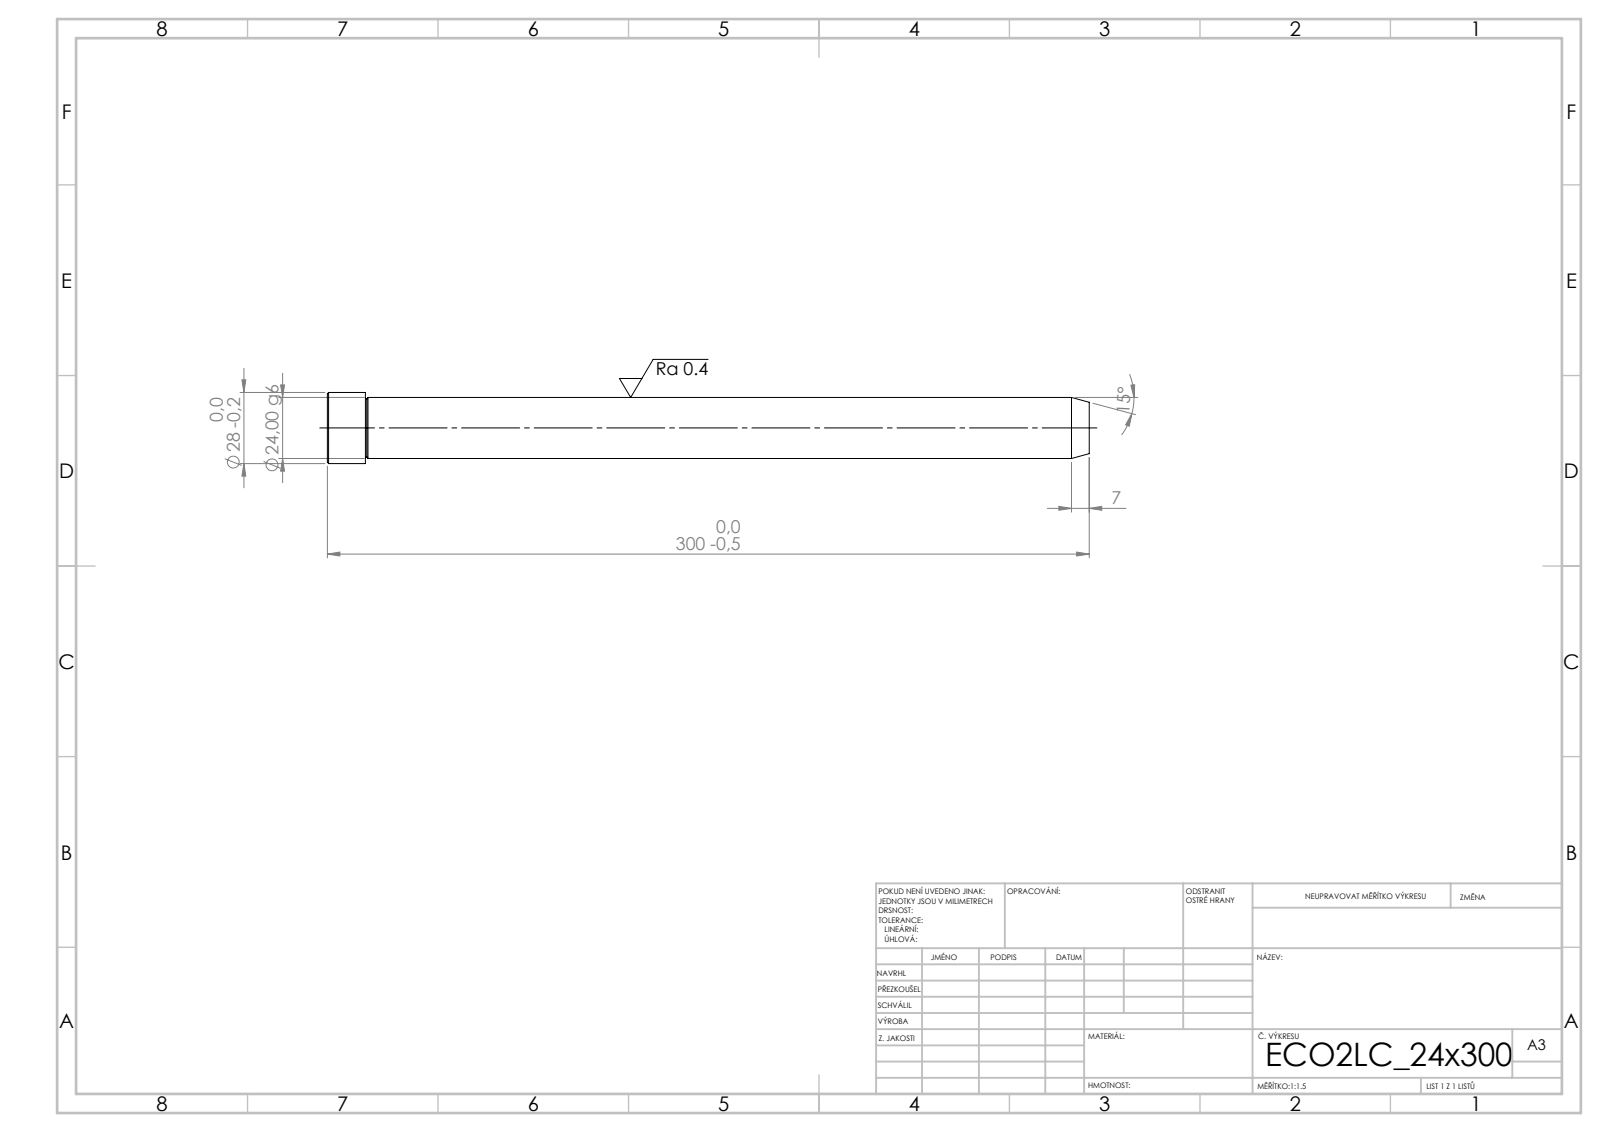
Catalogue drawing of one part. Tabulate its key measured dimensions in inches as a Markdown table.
| quantity | value |
| --- | --- |
| STEP written by | SolidWorks 2019 (CONFIG_CONTROL_DESIGN) |
| units | inches |
| bodies | 1 solid, 15 faces (3 planar, 4 cylindrical, 8 other) |
| overall size | 11.811 × 1.102 × 1.102 |
| volume | 8.4 in³ |
| surface area | 37.04 in² |
| round bosses / shafts (diameter × count) | 1.102 × 1, 0.945 × 1 |
| main face-to-face distances | 11.811, 11.22, 0.591 |
